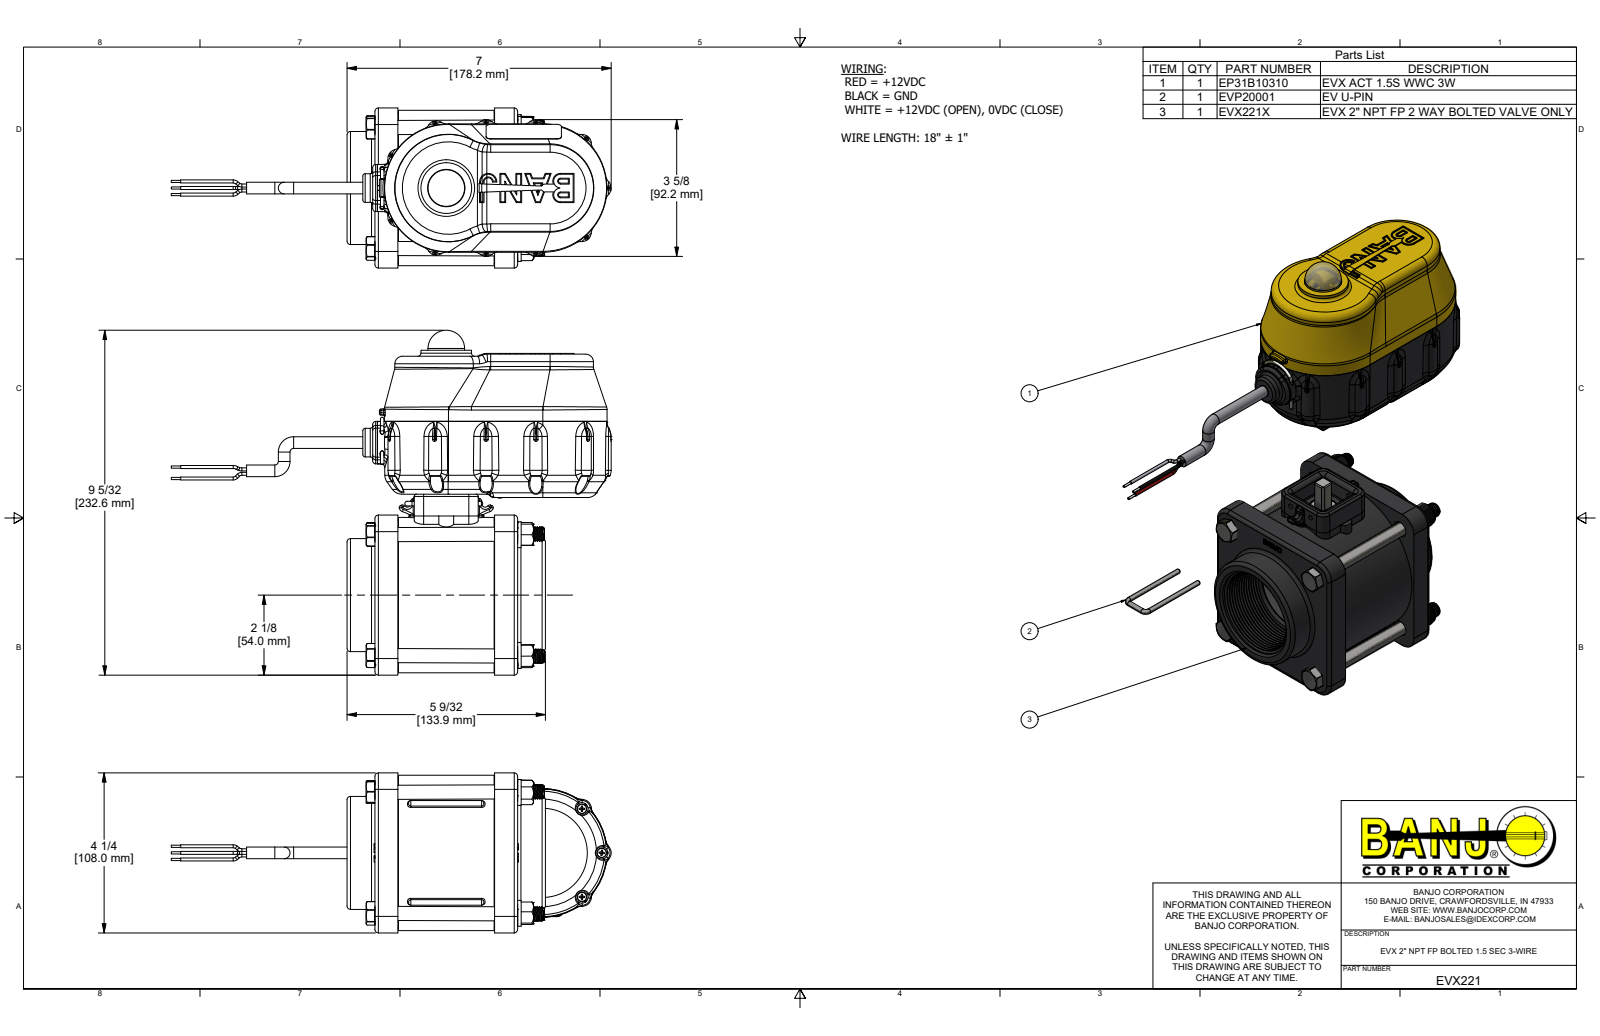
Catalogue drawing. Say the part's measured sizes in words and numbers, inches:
The part is named "EVX221; EVX221X; MEVX25254A; MEVX25254AX (+8 more)". Its 3-D file was written by "Autodesk Inventor 2022 (AUTOMOTIVE_DESIGN)". It is 95 solids with 11570 faces: 2995 planar, 3384 cylindrical and 5191 other. Overall it measures 11.685 by 9.157 by 4.25 inches. Its volume is 70.8 cubic inches and its surface area 748.8 square inches. Round holes: 11 of diameter 0.095, 11 of diameter 0.15, 8 of diameter 0.307, 8 of diameter 0.375, 7 of diameter 0.08, 4 of diameter 0.107, 4 of diameter 0.126, 4 of diameter 0.135, 4 of diameter 0.136, 4 of diameter 0.148, 4 of diameter 0.15, 4 of diameter 0.17. Round bosses or shafts: 60 of diameter 0.324, 17 of diameter 0.25, 15 of diameter 0.08, 11 of diameter 0.14, 11 of diameter 0.108, 11 of diameter 0.085, 6 of diameter 0.058, 5 of diameter 0.375. Partial cylindrical surfaces (rounded edges, fillets, slot ends): 180 of radius 0.013, 145 of radius 0.04, 99 of radius 0.01, 96 of radius 0.02, 57 of radius 0.005, 47 of radius 0.03, 33 of radius 0.015, 28 of radius 0.08. The main face-to-face distances are 0.1, 2.565, 0.06, 0.61, 3.18, 0.729, 2.485, 0.695, 3.095, 0.085. The hole center spacings are 1.662, 2.458, 2.656, 2.69, 2.715, 1.774, 2.73, 3.789.
